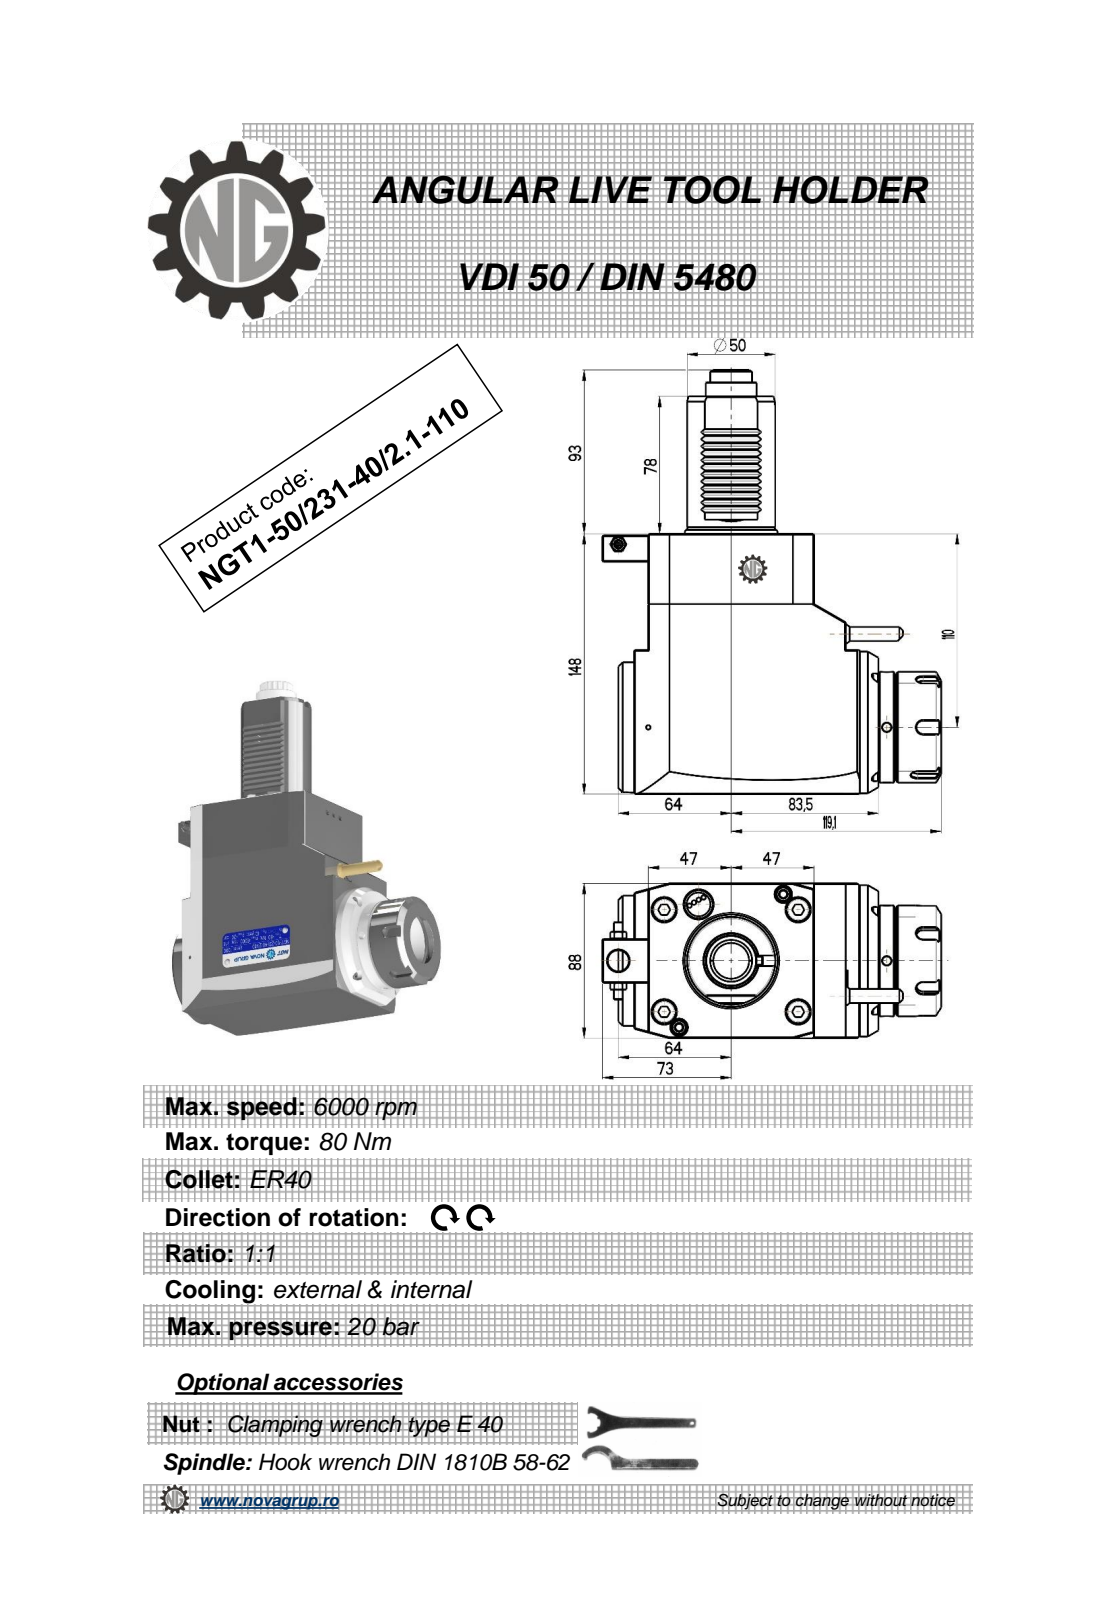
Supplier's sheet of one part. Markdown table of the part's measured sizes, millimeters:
| quantity | value |
| --- | --- |
| part name | NGT1_50_231_40_1_1_110 |
| STEP written by | PRO/ENGINEER BY PARAMETRIC TECHNOLOGY CORPORATION, 2010280 (CONFIG_CONTROL_DESIGN) |
| units | millimeters |
| bodies | 1 solid, 516 faces (206 planar, 161 cylindrical, 149 other) |
| overall size | 241 × 192.1 × 88 |
| volume | 1 842 000 mm³ |
| surface area | 114 530 mm² |
| round holes (diameter × count) | 5 × 3, 3 × 1, 4.2 × 1, 9.5 × 1, 12 × 1, 33.5 × 1 |
| round bosses / shafts (diameter × count) | 86 × 1, 74 × 1, 63 × 1, 51 × 1, 50 × 1, 28.8 × 1, 10 × 1, 8.96 × 1 |
| partial cylindrical surfaces (radius × count) | 3.04 × 36, 0.26 × 12, 0.3 × 12, 0.2 × 6, 3.75 × 5, 10.56 × 1, 11.88 × 1, 17.5 × 1 |
| main face-to-face distances | 88, 148, 94, 147.5, 17, 8, 9, 111, 120, 36.5 |
| hole center spacings | 52.46, 56.65, 101.5, 152.25, 184.38 |
